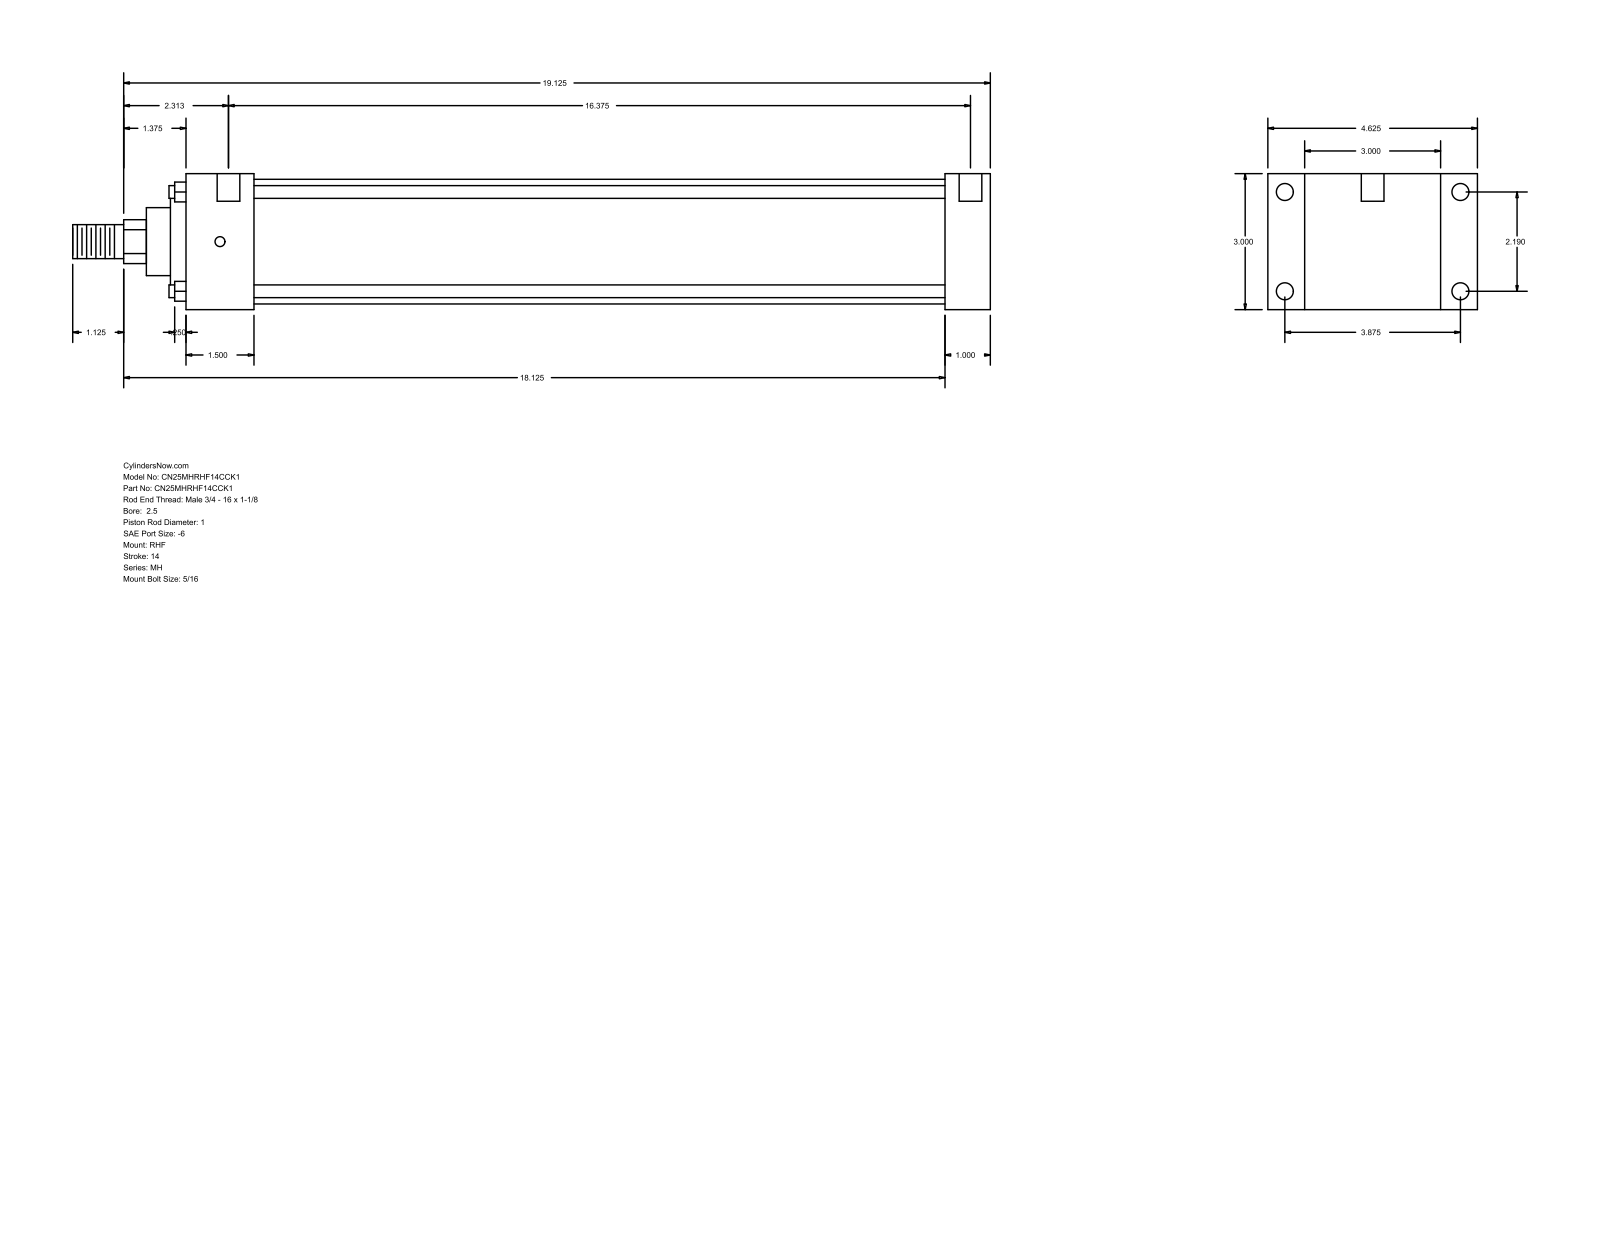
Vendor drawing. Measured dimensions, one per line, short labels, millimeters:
name: MH_RHF__0250_1
written by: GSSL Pune (CONFIG_CONTROL_DESIGN)
unit: mm
bodies: 0 solids, 90 faces (61 planar, 29 cylindrical, 0 other)
size: 514.35 × 117.47 × 76.2
holes: 4× ⌀5.56, 4× ⌀9.53, 2× ⌀12.7
bosses: 4× ⌀7.14, 1× ⌀69.85, 1× ⌀60.33, 1× ⌀38.1, 1× ⌀25.4, 1× ⌀19.05
rounds: 1× R12.29
face distances: 76.2, 25.39, 20.64, 96.84, 450.85, 425.46, 117.48, 38.11, 387.35, 412.74
hole spacings: 55.62, 98.42, 113.05, 423.86, 3.18, 4.76, 415.92, 419.1
